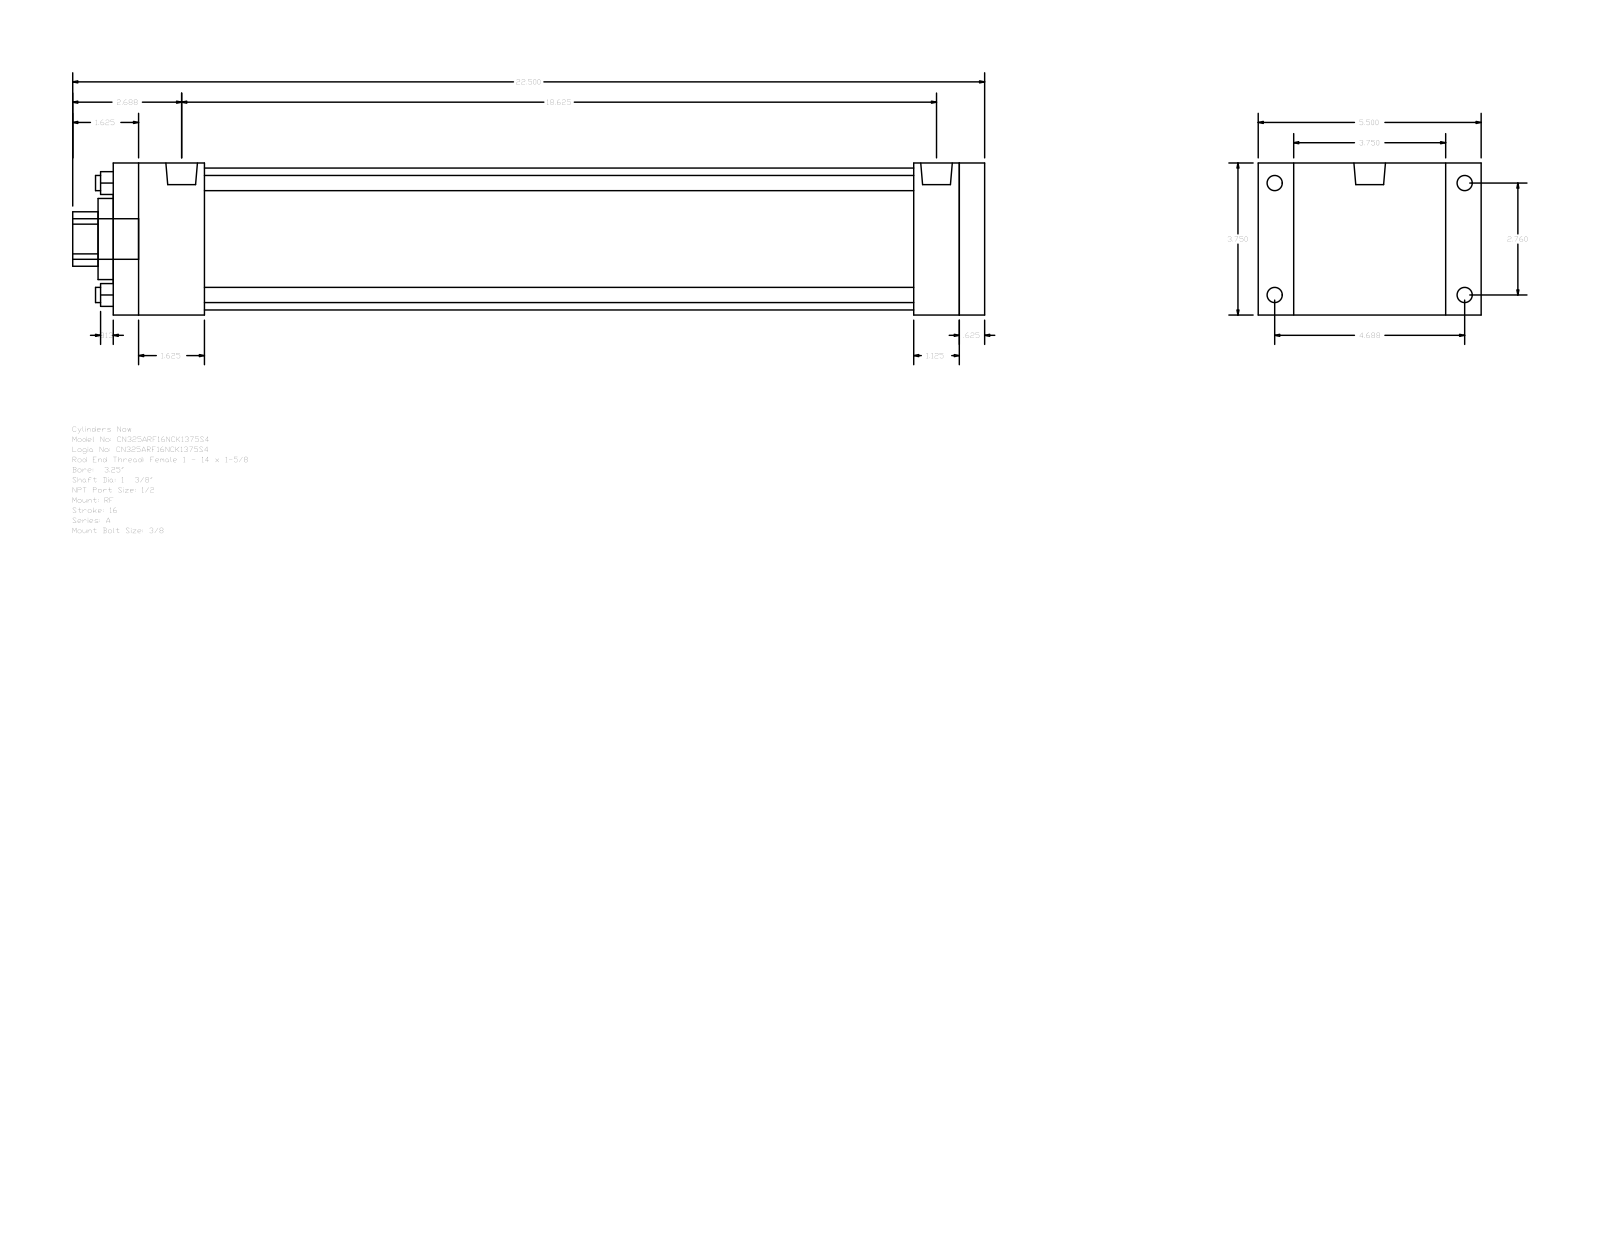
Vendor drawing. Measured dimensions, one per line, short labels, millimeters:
name: A_RF__0325_1.375
written by: GSSL Pune (CONFIG_CONTROL_DESIGN)
unit: mm
bodies: 0 solids, 92 faces (64 planar, 28 cylindrical, 0 other)
size: 571.5 × 139.7 × 95.25
holes: 4× ⌀9.53, 1× ⌀34.92, 1× ⌀50.8, 1× ⌀88.9
bosses: 4× ⌀9.53, 4× ⌀8.73, 2× ⌀19.77, 1× ⌀25.4
rounds: 1× R17.06
face distances: 95.24, 546.1, 15.88, 530.22, 22.23, 117.47, 28.57, 501.65, 44.45, 57.15
hole spacings: 49.57, 70.1, 99.14
